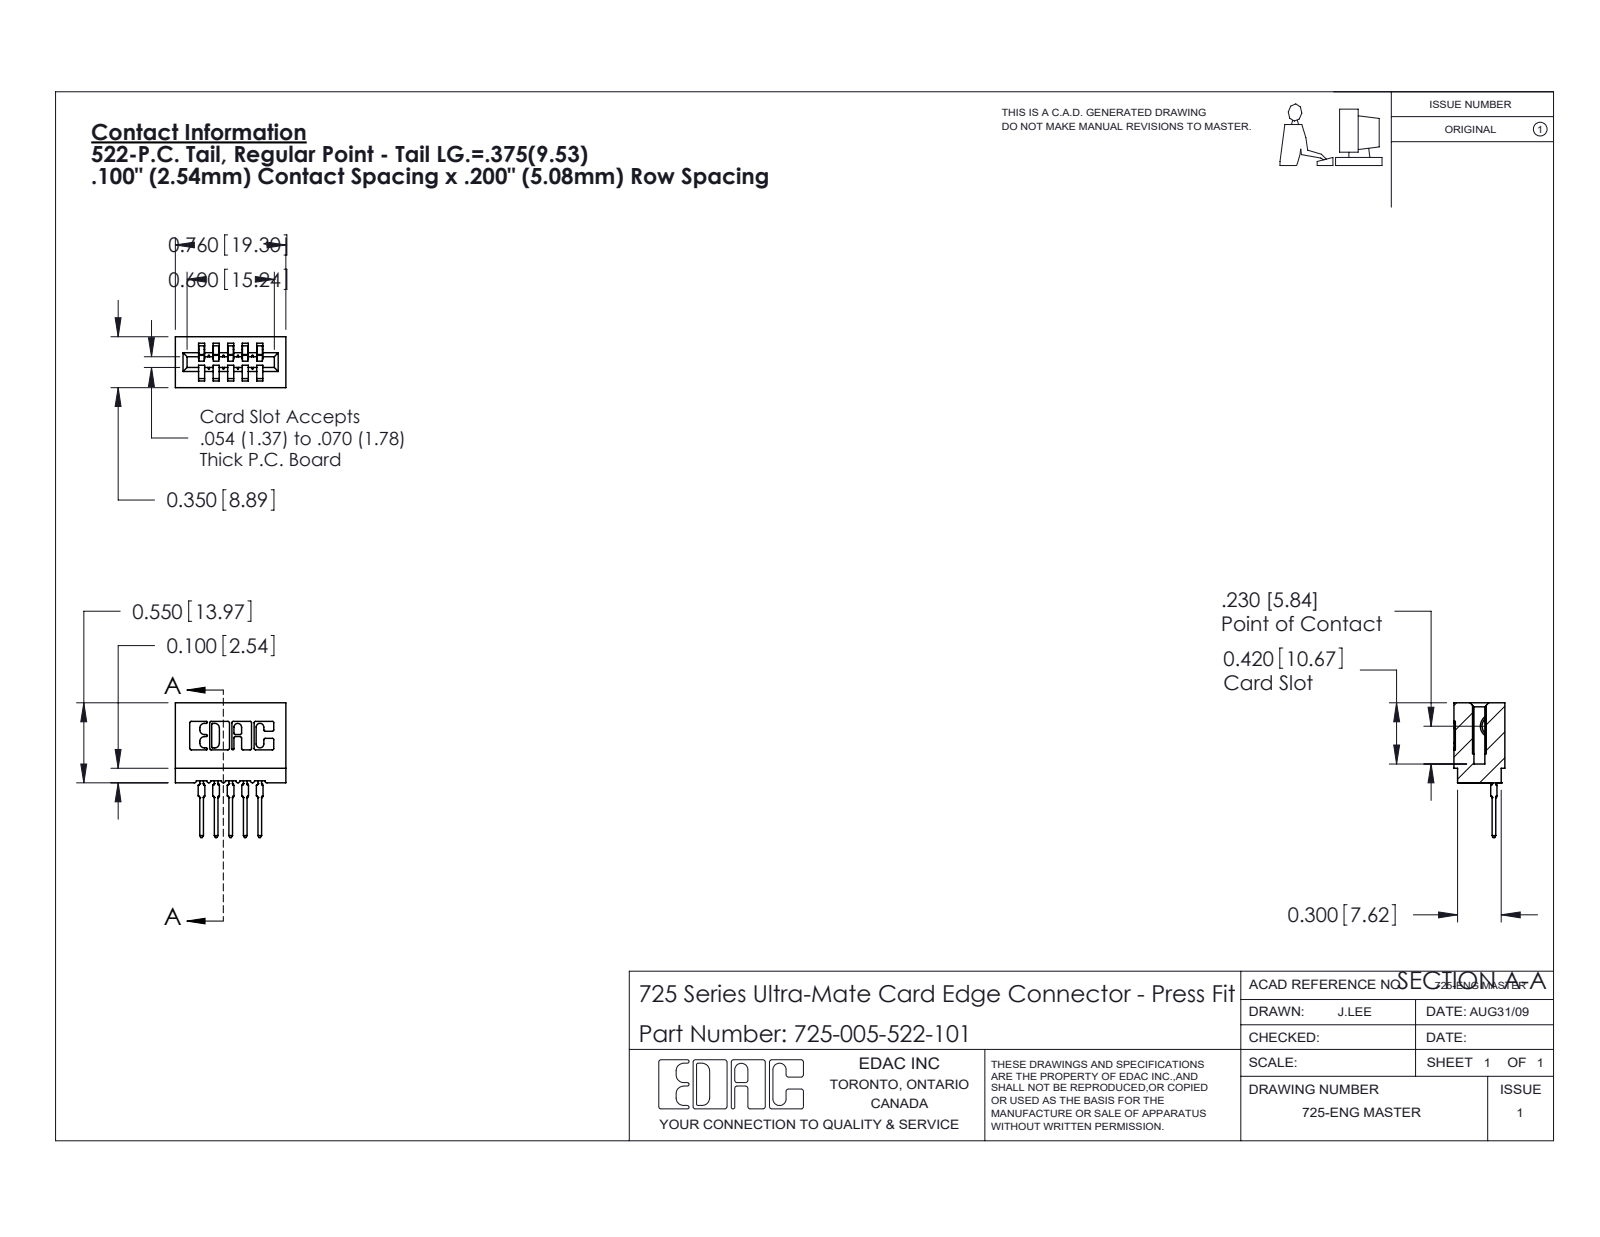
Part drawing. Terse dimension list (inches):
name: 745-292-001_522; 725 Part_Insulator Option - 01; 725-005-522-101
written by: SolidWorks 2020 (CONFIG_CONTROL_DESIGN)
unit: in
bodies: 6 solids, 655 faces (390 planar, 135 cylindrical, 130 other)
size: 0.926 × 0.76 × 0.35
volume: 0.102 in³; area: 3.975 in²
rounds: 22× R0.01, 10× R0.015, 10× R0.021, 6× R0.007, 6× R0.031, 4× R0.005, 4× R0.011, 3× R0.026
face distances: 0.1, 0.2, 0.042, 0.3, 0.142, 0.058, 0.242, 0.158, 0.212, 0.35
